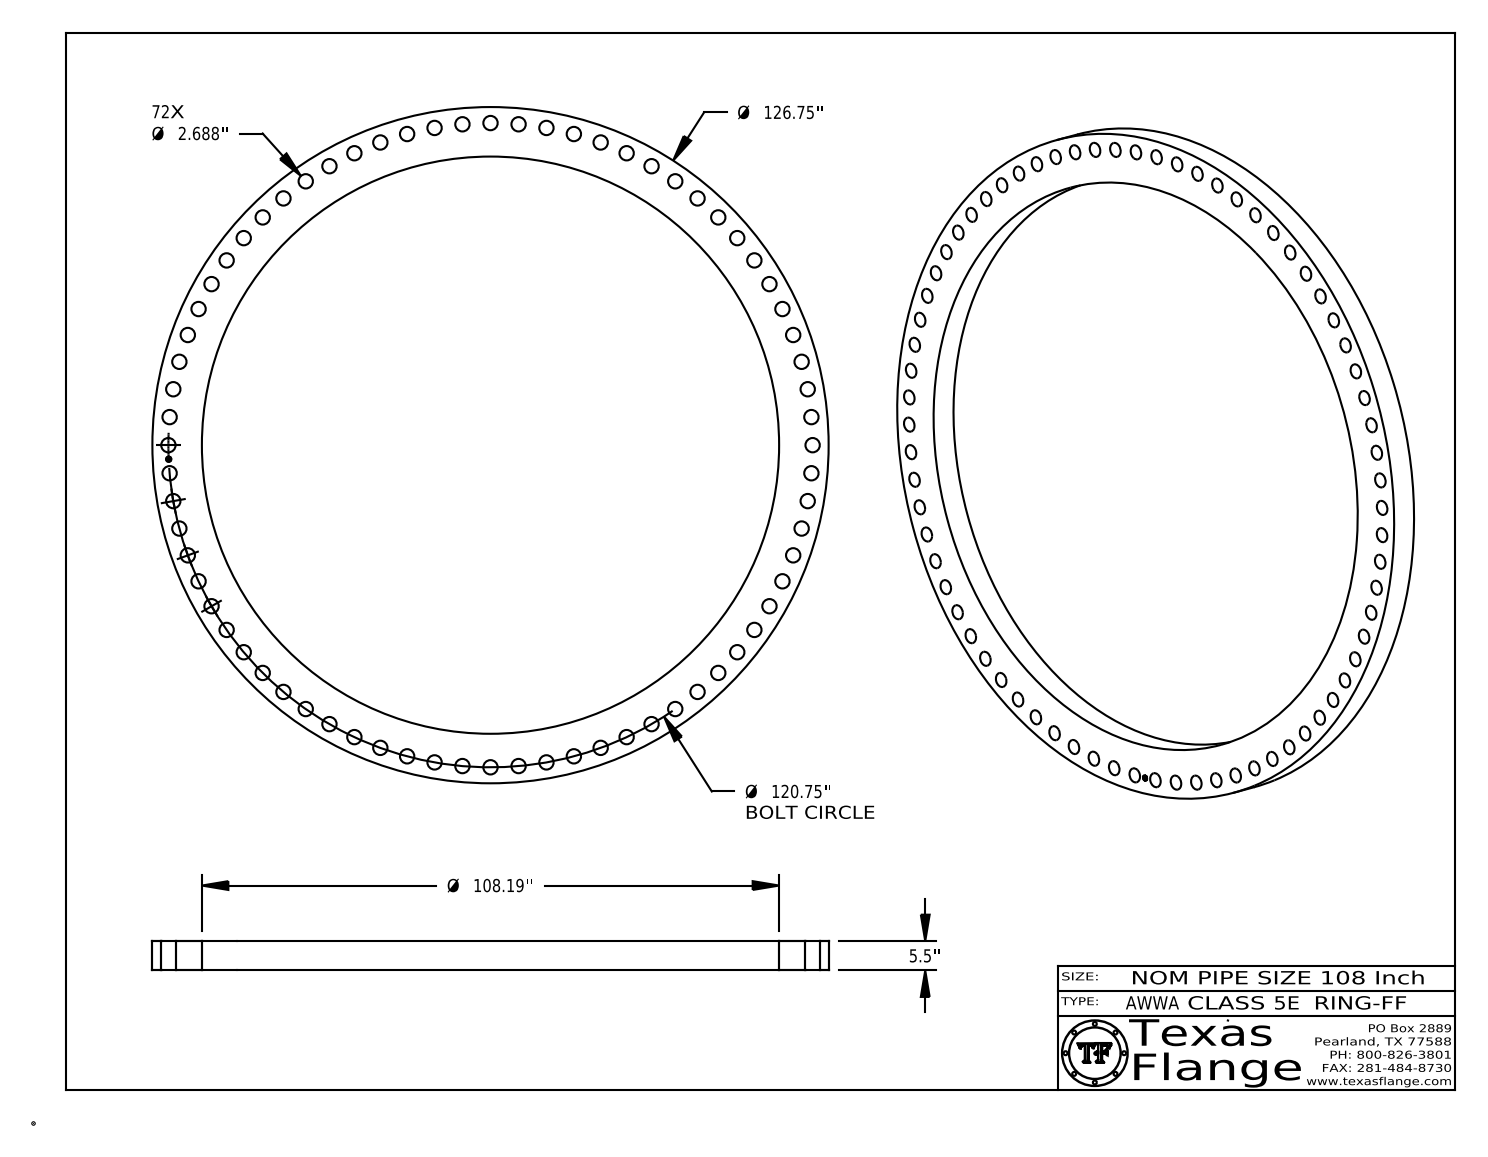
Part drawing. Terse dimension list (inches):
name: AWWA Class 5E-RING-FF
written by: CATIA V5 STEP AP214 (AUTOMOTIVE_DESIGN)
unit: in
bodies: 1 solid, 535 faces (367 planar, 168 cylindrical, 0 other)
size: 126.75 × 126.75 × 5.5
volume: 16 589 in³; area: 13 436 in²
holes: 72× ⌀2.688, 1× ⌀1, 1× ⌀108.19
bosses: 8× ⌀0.061, 1× ⌀126.75, 1× ⌀0.788
face distances: 5.5, 0.015, 5.485, 0.298, 0.292, 0.054, 0.194, 0.248, 0.044, 0.15
hole spacings: 60.375, 10.524, 5.267, 60.375, 31.252, 20.968, 26.135, 41.299
